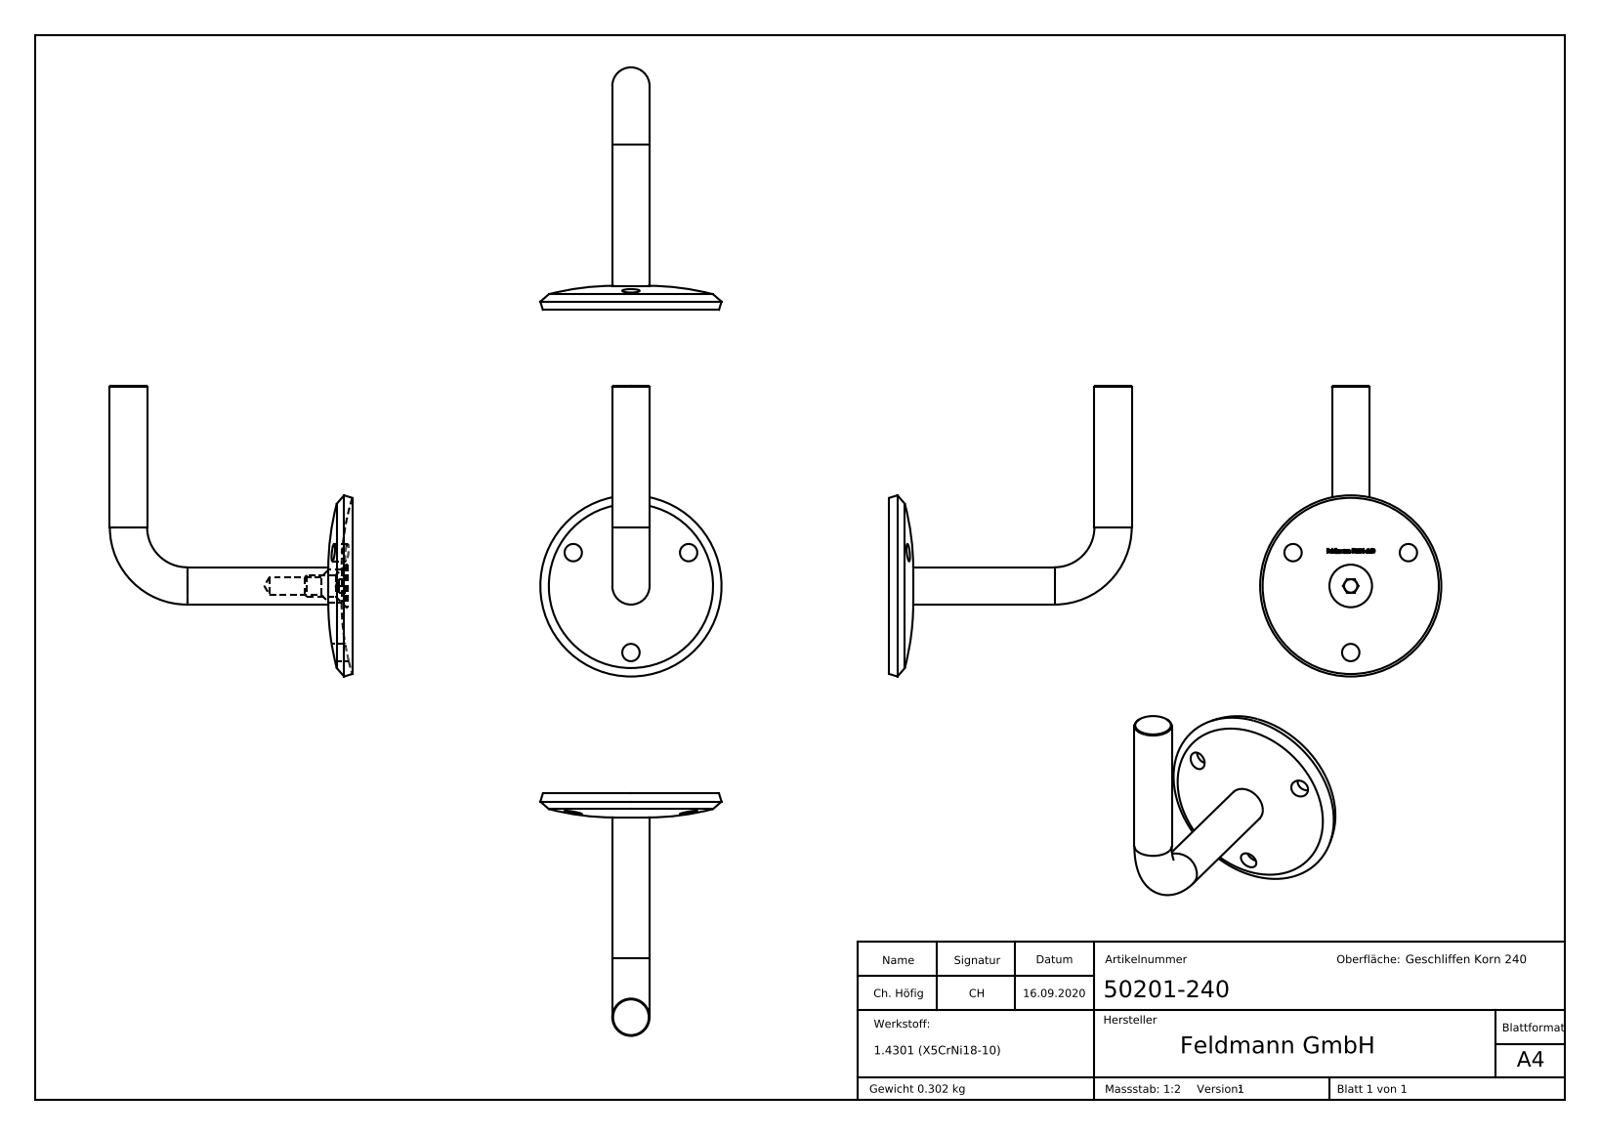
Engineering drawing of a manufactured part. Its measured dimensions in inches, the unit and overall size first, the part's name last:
Units: inches
Overall size (bounding box): 4.291 × 3.583 × 2.677
Round holes (diameter × count): ⌀0.256 ×3, ⌀0.268 ×1, ⌀0.492 ×1
Round bosses / shafts (diameter × count): ⌀0.551 ×2, ⌀0.63 ×1, ⌀0.315 ×1
Main face-to-face distances: 0.281, 0.63, 0.348, 0.197, 2.854, 3.051, 0.118, 0.163, 0.512, 0.394
Hole centre spacings: 0.984, 1.705
Volume: 2.332 in³ · Surface area: 24.62 in²
Bodies: 3 solids, 270 faces (111 planar, 18 cylindrical, 141 other)
Part name (STEP PRODUCT): 50201-240 Teil2; 50201-240 Teil1; DIN-7991 M3-M10_DIN7991 M8x16; 50201-240 (+3 more)
STEP written by: SolidWorks 2018 (CONFIG_CONTROL_DESIGN)
